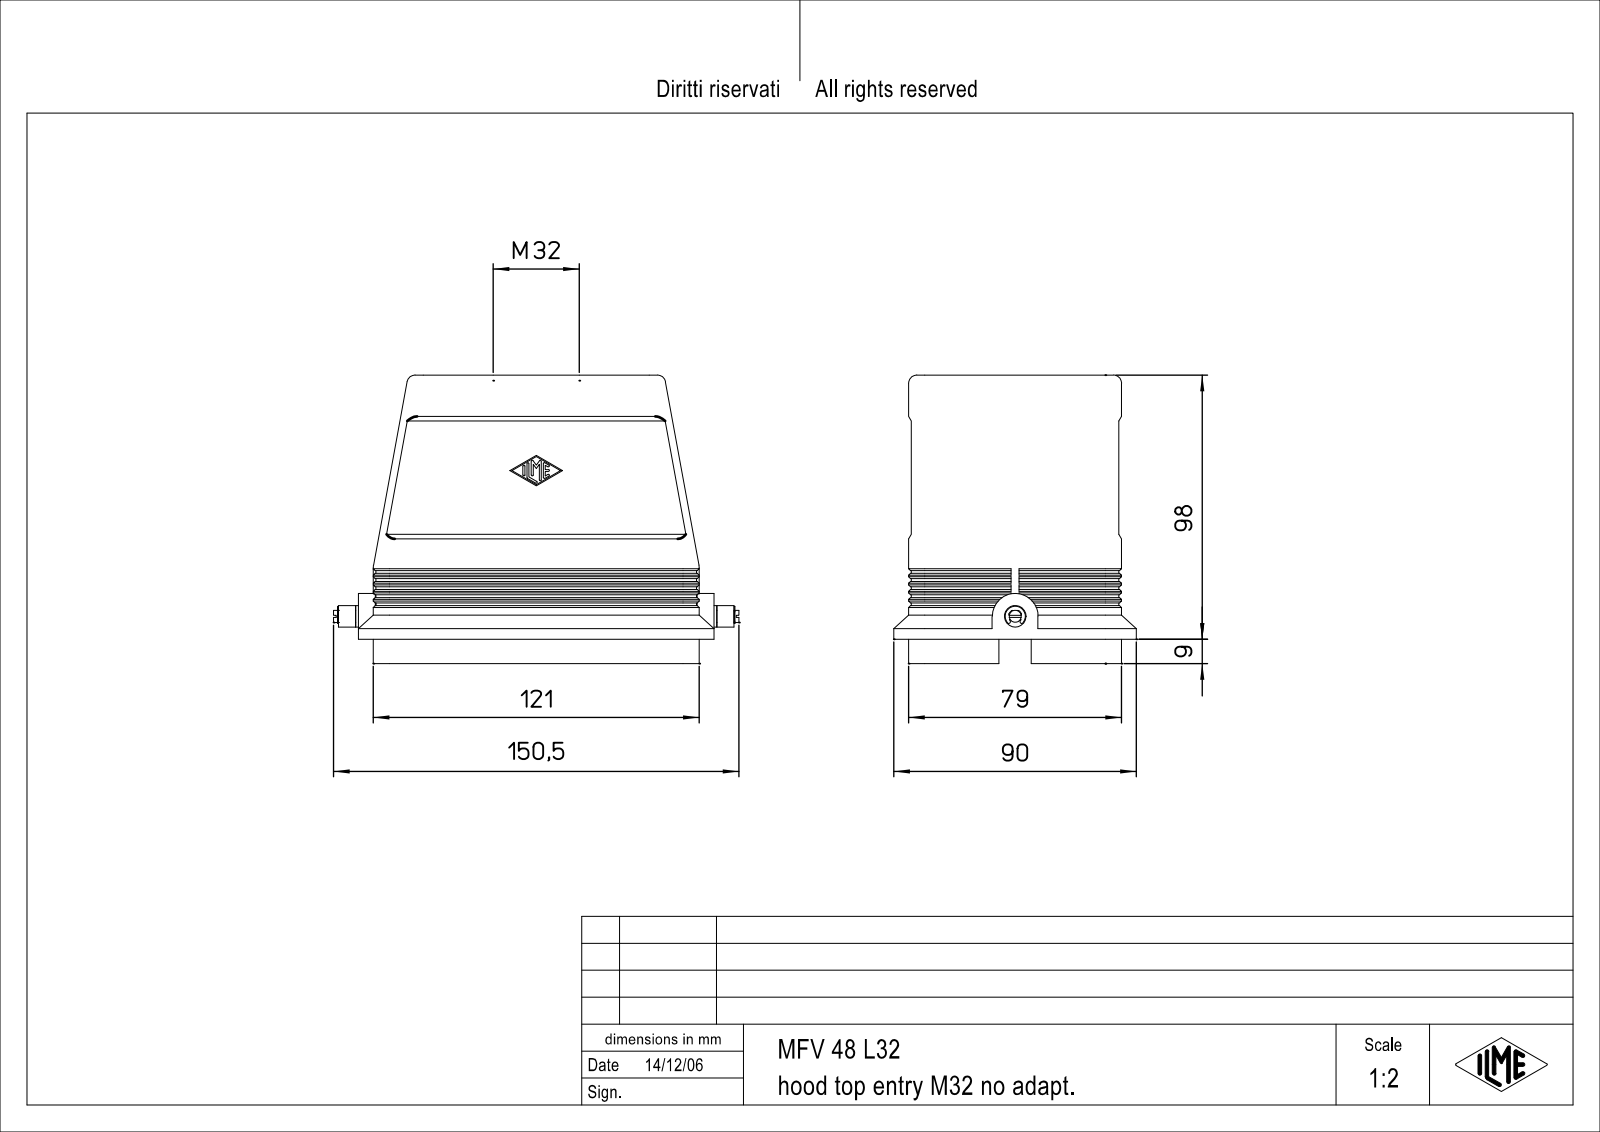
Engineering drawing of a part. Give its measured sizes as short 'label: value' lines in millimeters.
name: CH_MH Tüllengehäuse Verschluss für 1 Bügel 104_62 Teil 2
written by: Autodesk Inventor 7 (AUTOMOTIVE_DESIGN)
unit: mm
bodies: 1 solid, 672 faces (246 planar, 177 cylindrical, 249 other)
size: 150.5 × 118 × 90
volume: 233 863 mm³; area: 107 390 mm²
holes: 4× ⌀2.46, 4× ⌀3.5, 1× ⌀32, 1× ⌀47
bosses: 1× ⌀8, 1× ⌀6, 1× ⌀4.5, 1× ⌀3.5
rounds: 14× R0.38, 12× R2, 10× R6, 4× R0.5, 4× R3, 4× R11.5, 3× R0.95, 2× R0.62
face distances: 3.5, 72, 75.5, 1, 109, 2.5, 10, 79, 74.5, 78
hole spacings: 27, 52.15, 60.54, 104, 107.45
